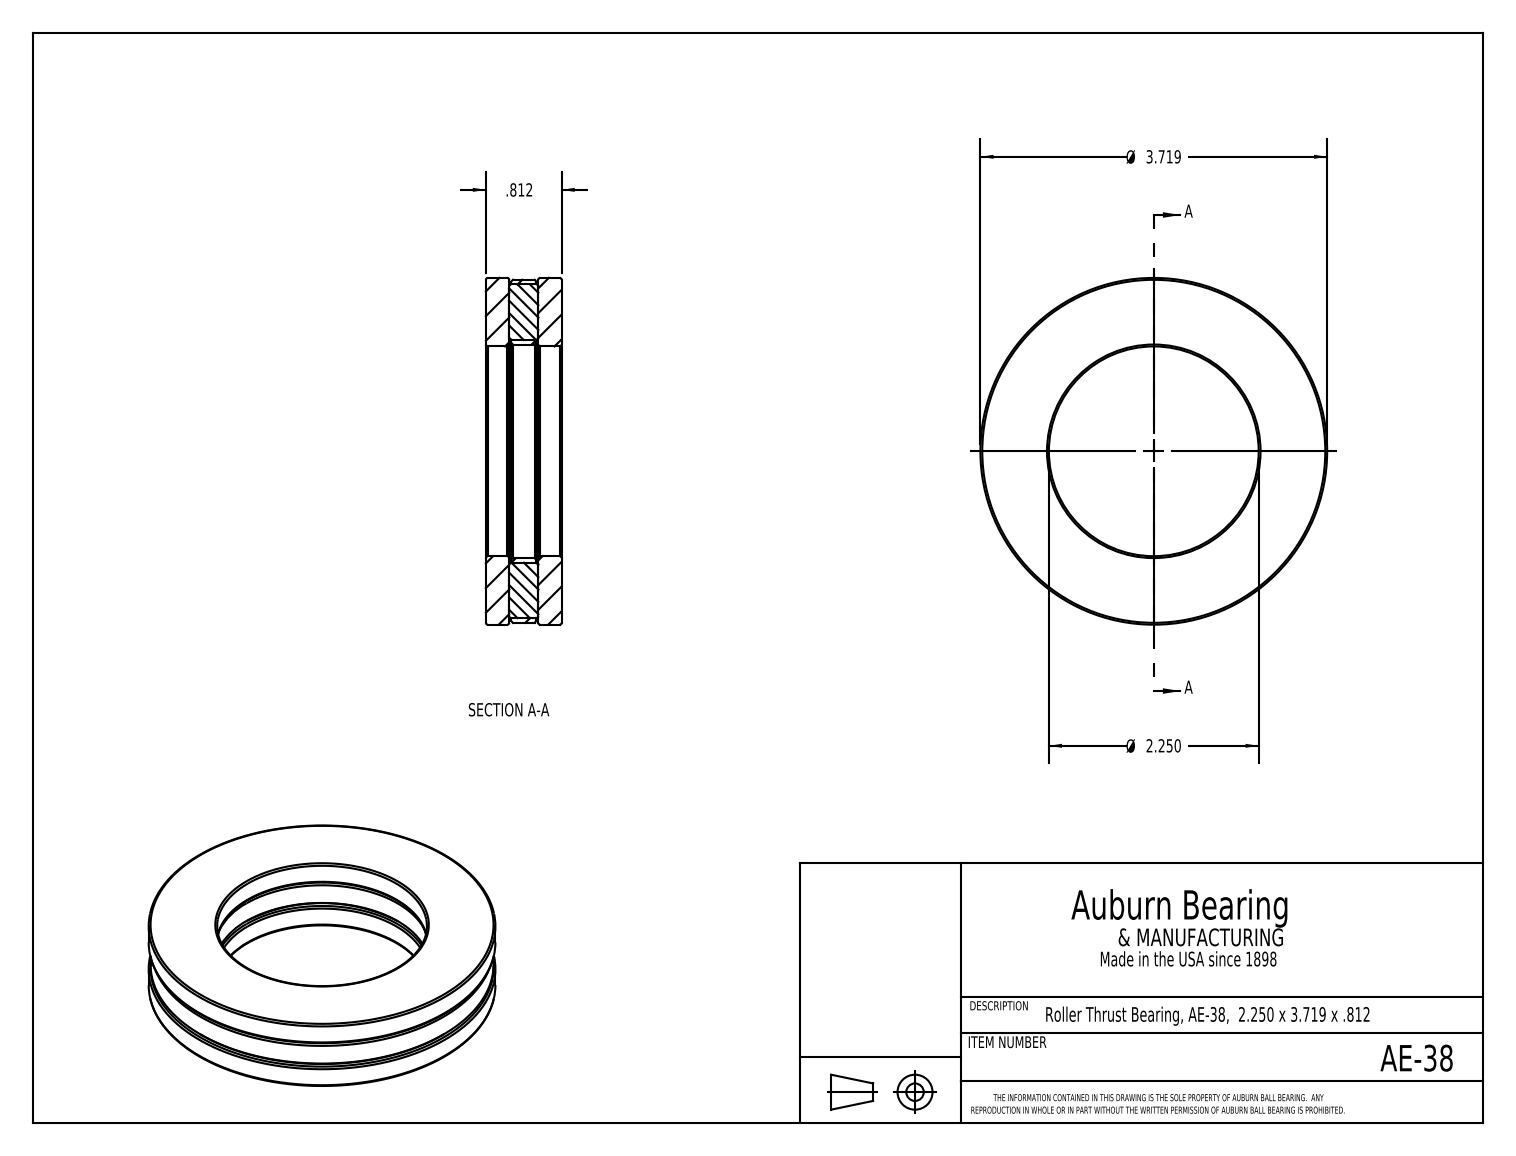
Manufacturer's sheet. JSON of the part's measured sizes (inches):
{"part_name": "AE-38", "step_written_by": "SolidWorks 2017 (CONFIG_CONTROL_DESIGN)", "units": "inches", "bodies": {"solids": 7, "faces": 60, "planar": 30, "cylindrical": 10, "other": 20}, "overall_size": [3.719, 3.719, 0.812], "volume_in3": 5.179, "surface_area_in2": 57.32, "round_holes": [[2.25, 1], [2.29, 1]], "round_bosses_or_shafts": [[0.312, 2], [3.719, 1], [3.679, 1]], "face_to_face_distances": [0.25, 0.562, 0.27, 0.542, 0.02, 0.292, 0.312, 0.812, 0.272, 1.039]}
